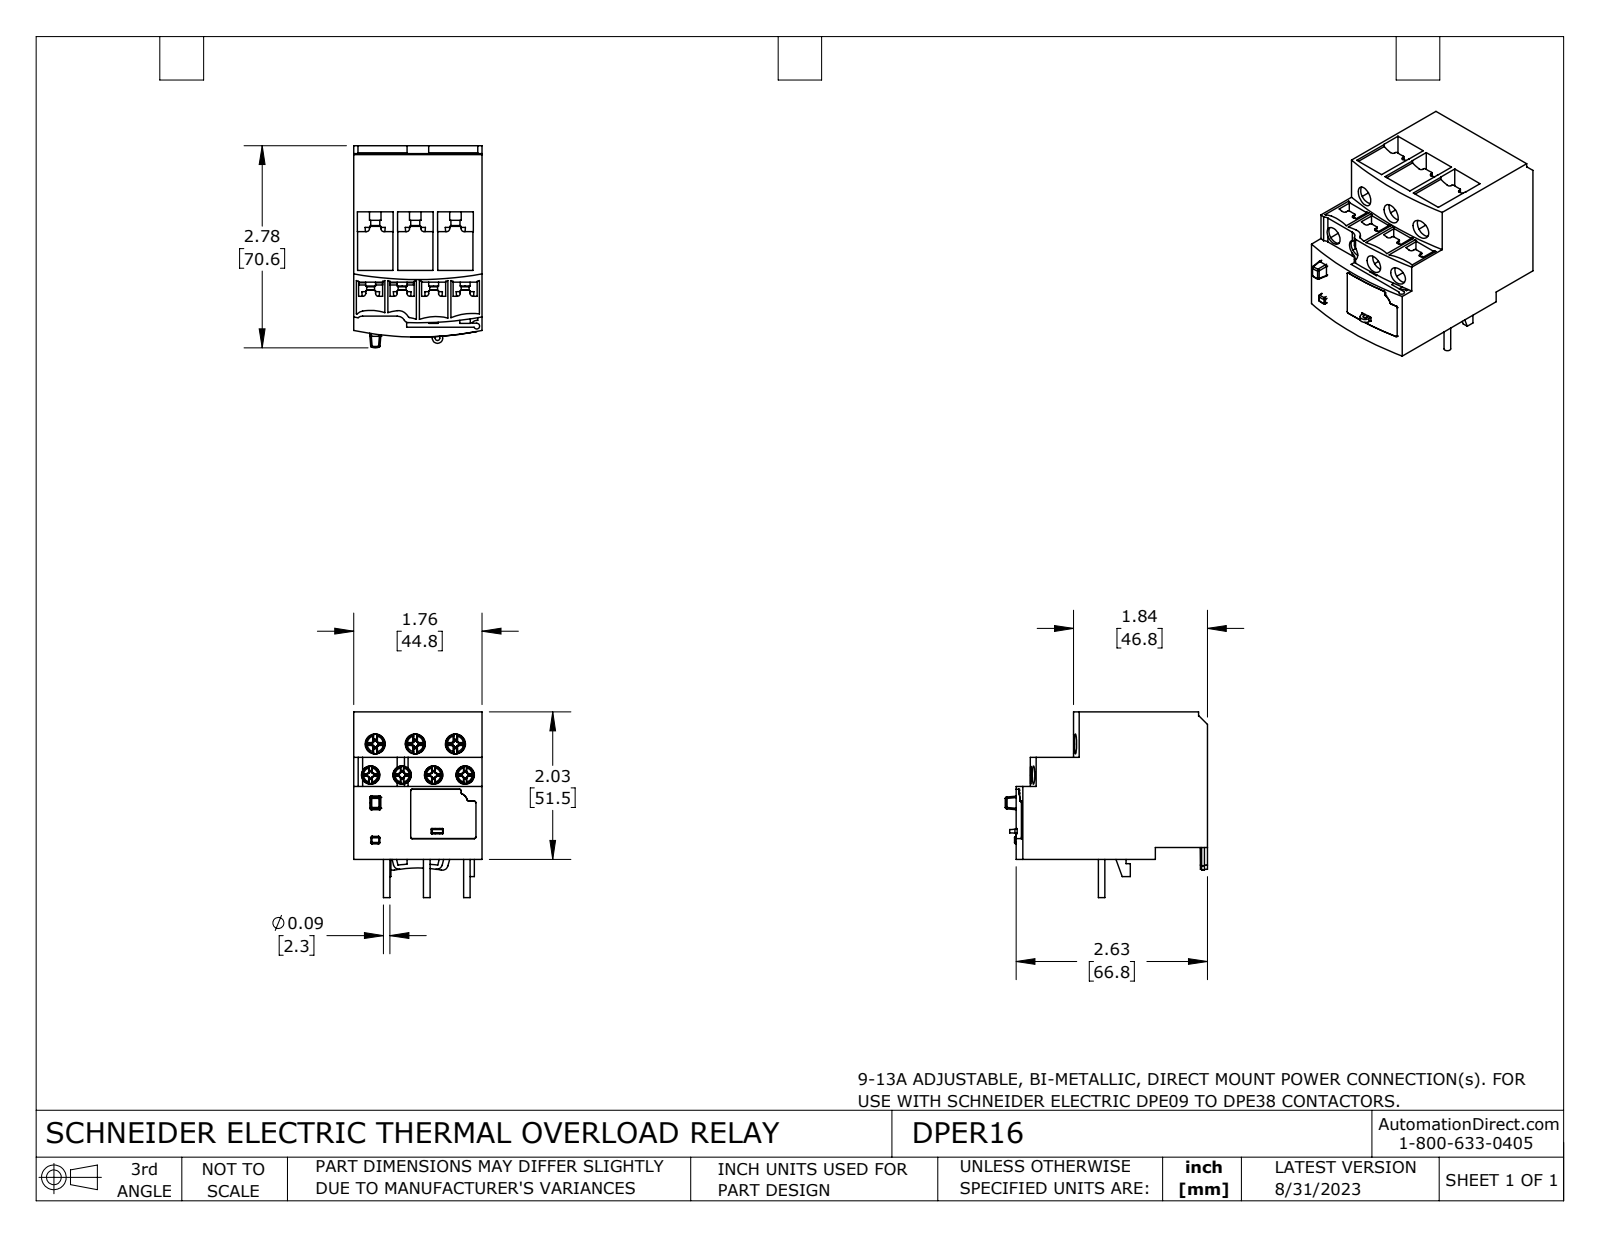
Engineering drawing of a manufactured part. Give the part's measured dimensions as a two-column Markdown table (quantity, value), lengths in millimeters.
| quantity | value |
| --- | --- |
| part name | DPER16 |
| STEP written by | SolidWorks 2021 (CONFIG_CONTROL_DESIGN) |
| units | millimeters |
| bodies | 16 solids, 1212 faces (676 planar, 269 cylindrical, 267 other) |
| overall size | 70.6 × 64.8 × 44.8 |
| volume | 113 900 mm³ |
| surface area | 30 420 mm² |
| round holes (diameter × count) | 6.4 × 4, 7 × 3, 2 × 2, 3 × 2, 1.5 × 1, 6.2 × 1 |
| round bosses / shafts (diameter × count) | 2.3 × 12, 3.5 × 4, 2.7 × 4, 4 × 3, 3.9 × 3, 3.1 × 3, 3 × 1, 2.7 × 1 |
| partial cylindrical surfaces (radius × count) | 0.5 × 52, 1 × 22, 0.1 × 19, 0.3 × 8, 0.2 × 6, 16 × 6, 2 × 4, 0.6 × 2 |
| main face-to-face distances | 44.8, 4.2, 51.5, 47.3, 23.1, 14, 15.7, 35.8, 31.6, 63.4 |
| hole center spacings | 11, 14, 22, 8.5, 9.7, 10.3, 10.7, 11.4 |
